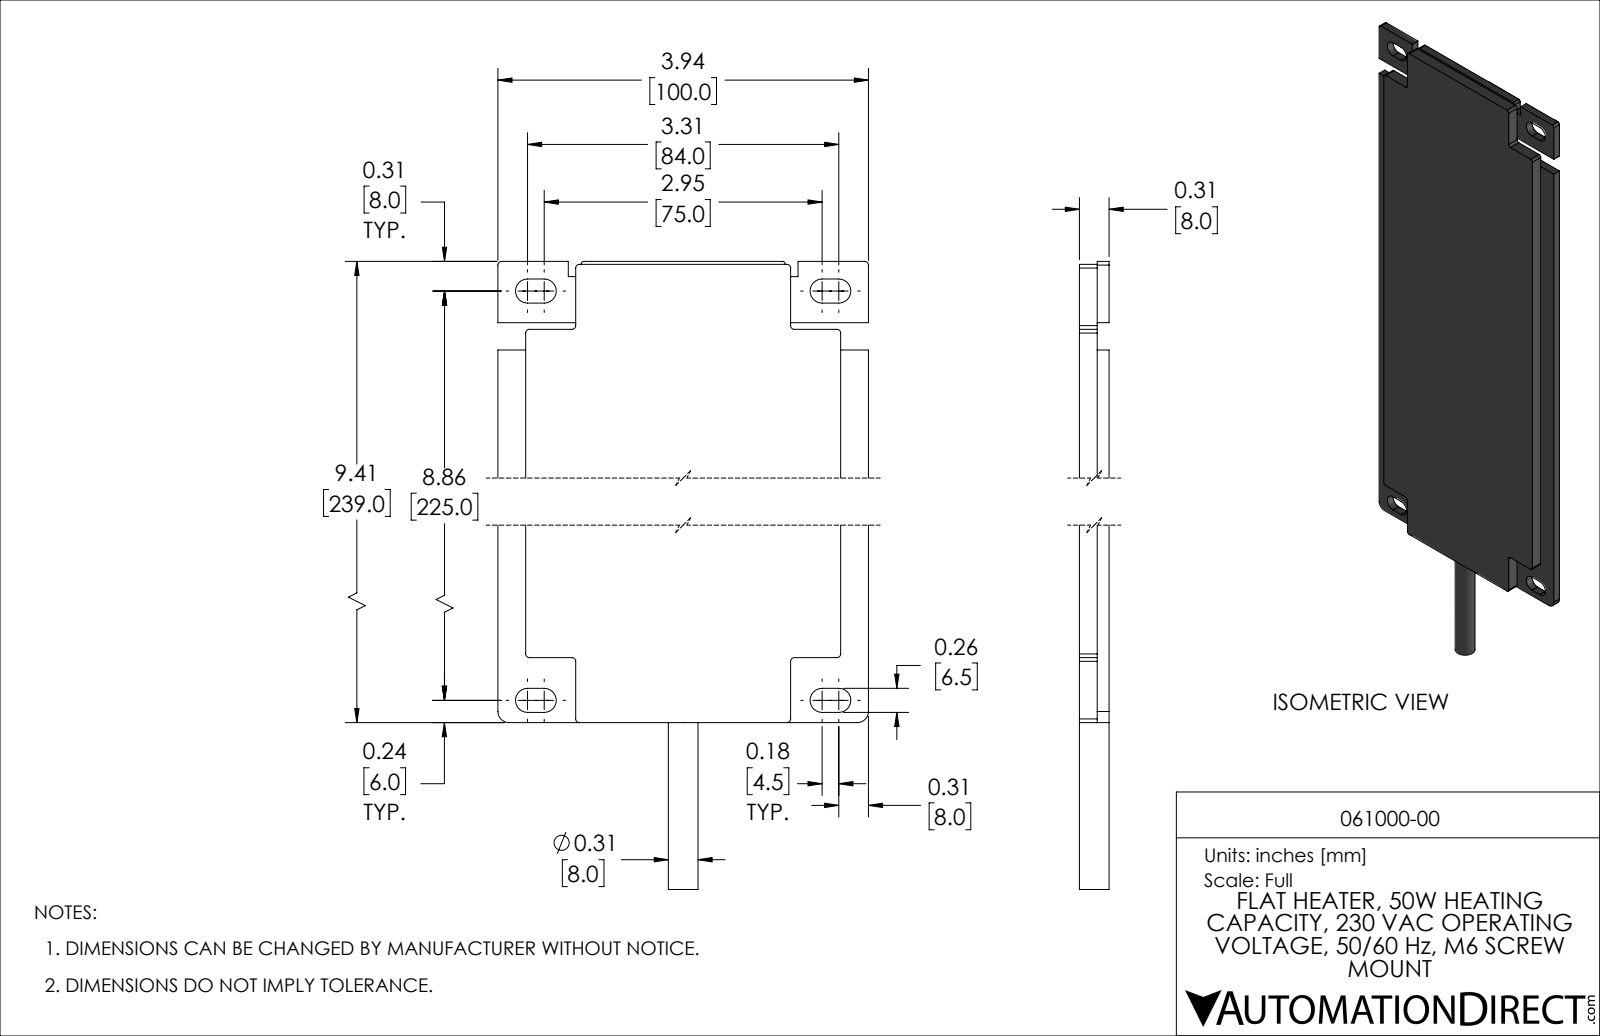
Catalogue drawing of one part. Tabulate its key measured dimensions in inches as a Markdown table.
| quantity | value |
| --- | --- |
| part name | PRODUCT_NAME_1 |
| STEP written by | ACIS (AUTOMOTIVE_DESIGN_CC2) |
| units | inches |
| bodies | 1 solid, 76 faces (48 planar, 28 cylindrical, 0 other) |
| overall size | 11.181 × 3.937 × 0.315 |
| volume | 10.26 in³ |
| surface area | 84.2 in² |
| round bosses / shafts (diameter × count) | 0.315 × 1 |
| partial cylindrical surfaces (radius × count) | 0.039 × 14, 0.128 × 8, 0.031 × 2, 0.118 × 2 |
| main face-to-face distances | 0.315, 0.189, 0.126, 0.295, 3.642, 3.346, 3.937, 8.469, 8.759, 0.29 |
